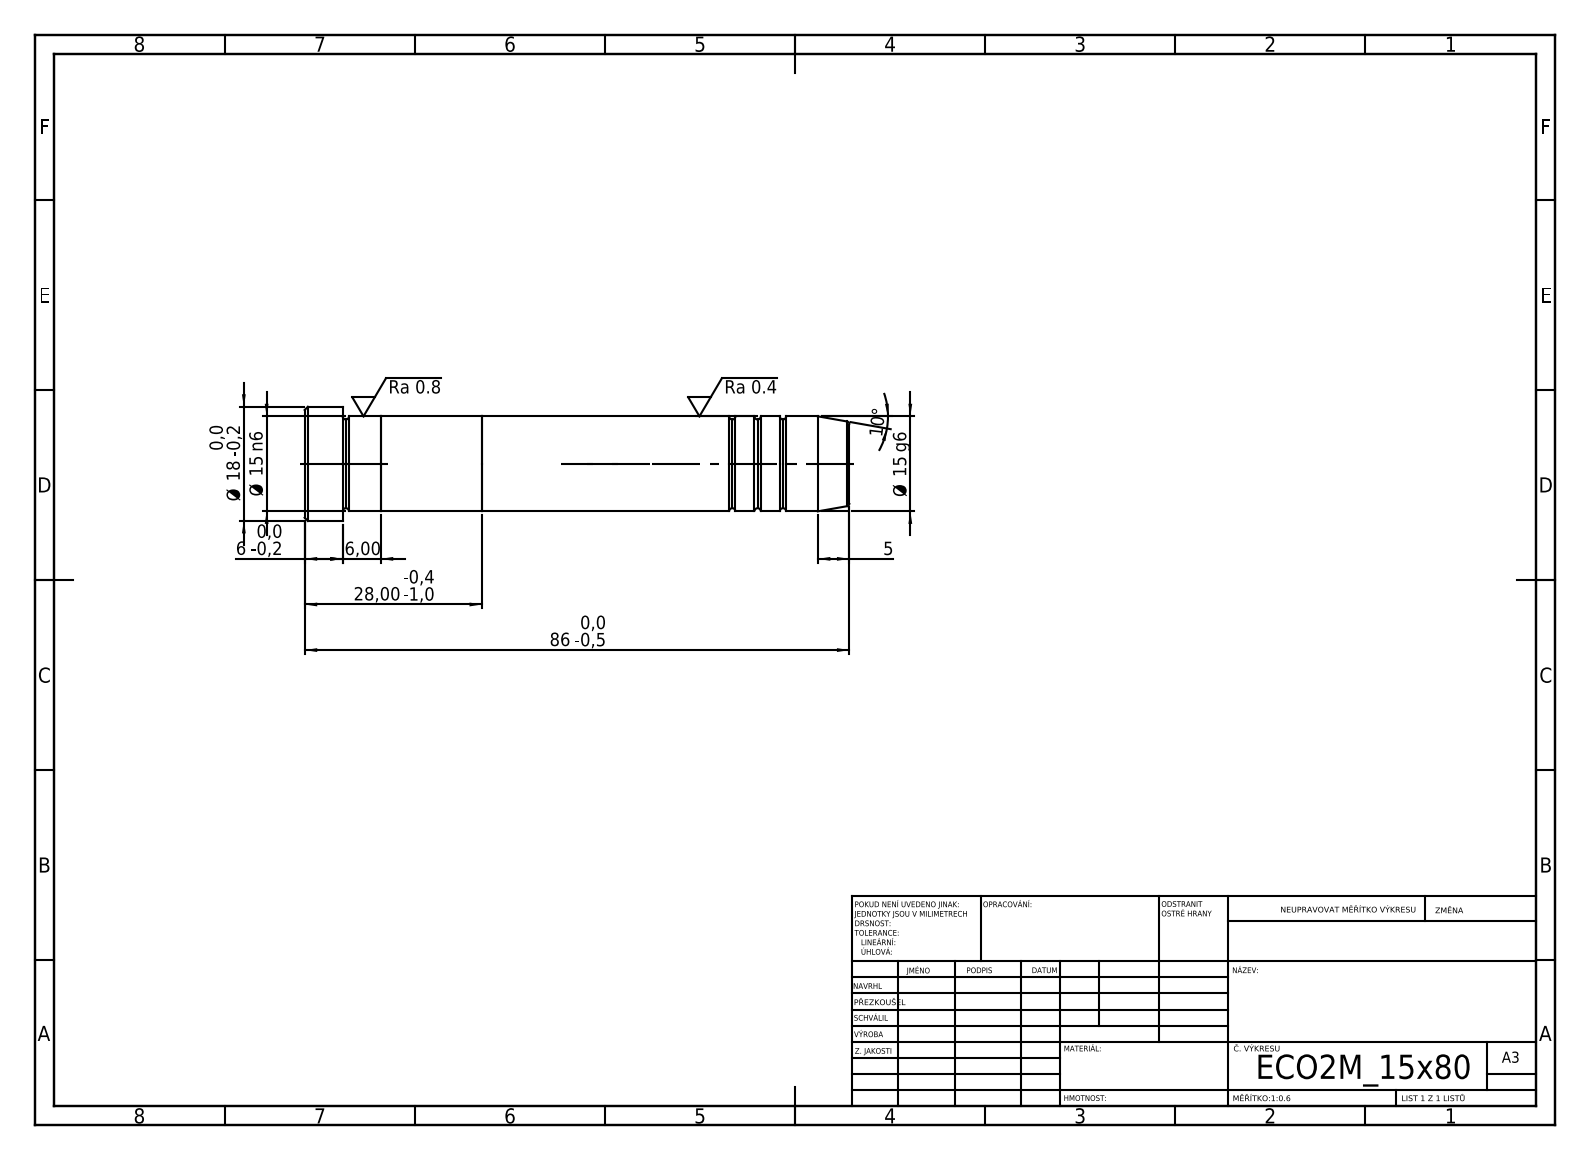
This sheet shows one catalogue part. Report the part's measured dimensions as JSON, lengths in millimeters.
{"step_written_by": "SolidWorks 2019 (CONFIG_CONTROL_DESIGN)", "units": "millimeters", "bodies": {"solids": 3, "faces": 43, "planar": 7, "cylindrical": 14, "other": 22}, "overall_size": [86, 18, 18], "volume_mm3": 15484, "surface_area_mm2": 5348, "round_bosses_or_shafts": [[18, 1], [15, 1]], "face_to_face_distances": [16, 28, 12, 6, 58, 74, 86, 80, 22]}
